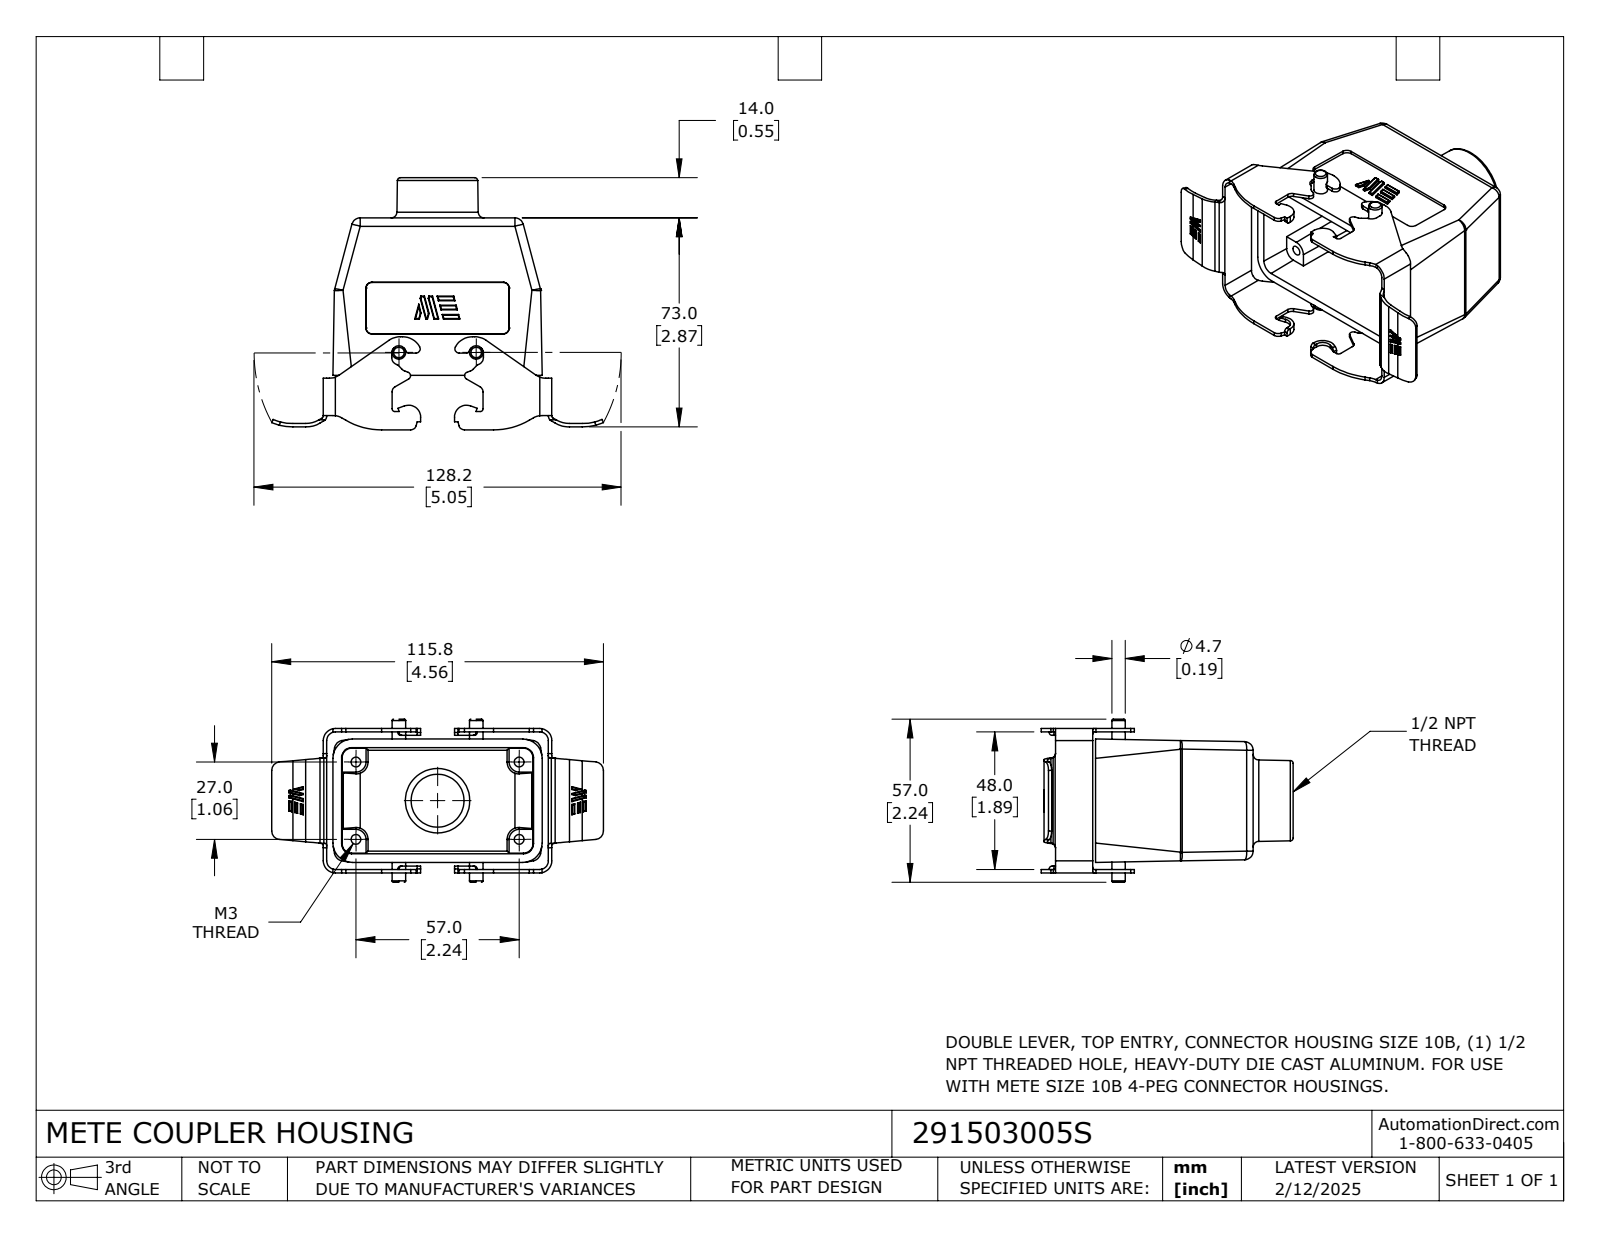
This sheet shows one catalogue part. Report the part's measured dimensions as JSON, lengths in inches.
{"part_name": "291503005S", "step_written_by": "SolidWorks 2024 (CONFIG_CONTROL_DESIGN)", "units": "inches", "bodies": {"solids": 1, "faces": 595, "planar": 243, "cylindrical": 274, "other": 78}, "overall_size": [4.559, 3.465, 2.244], "volume_in3": 3.413, "surface_area_in2": 62.78, "round_holes": [[0.134, 4], [0.728, 1]], "round_bosses_or_shafts": [[0.185, 2]], "partial_cylinders_radius": [[0.008, 75], [0.039, 20], [0.118, 18], [0.079, 14], [0.098, 8], [0.031, 6], [0.059, 6], [0.165, 6]], "face_to_face_distances": [0.118, 0.047, 1.937, 0.04, 0.078, 1.89, 0.447, 0.329, 1.984, 3.094], "hole_center_spacings": [1.242, 1.063, 2.244, 2.483]}
